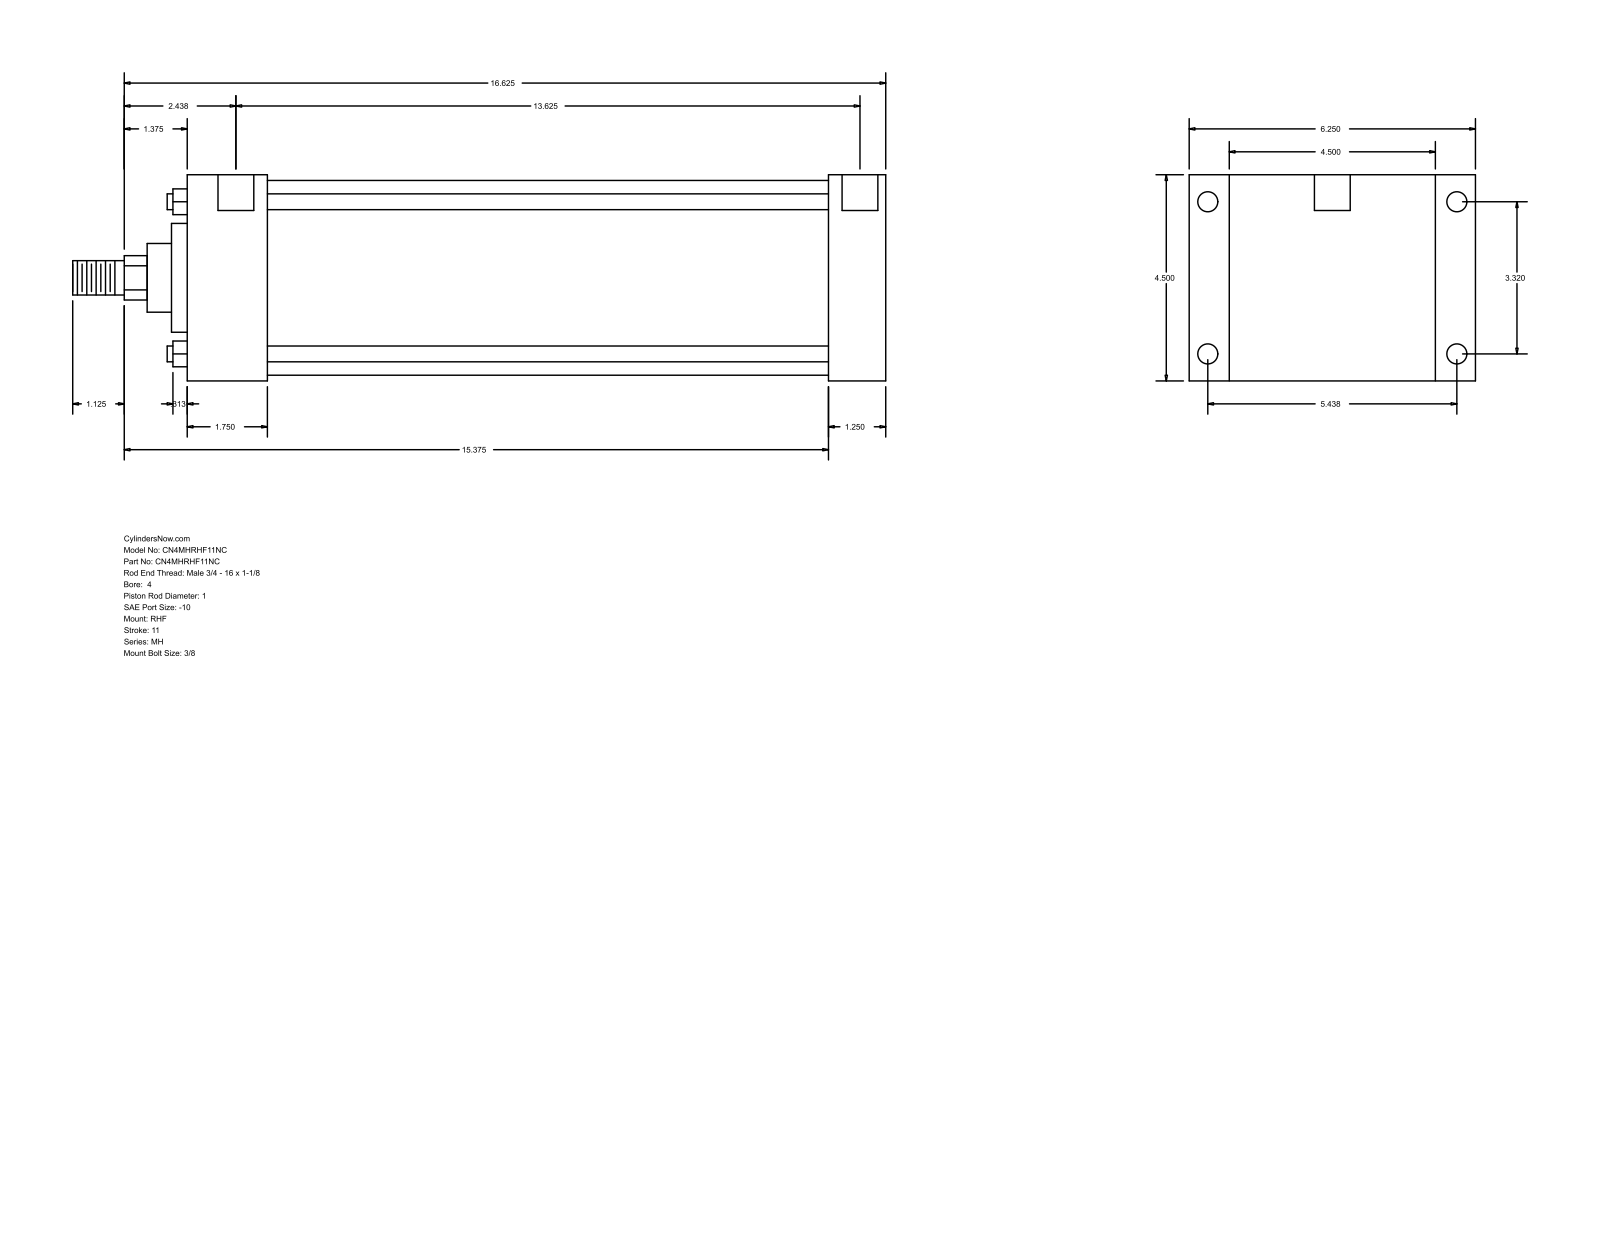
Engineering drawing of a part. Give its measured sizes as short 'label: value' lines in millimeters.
name: MH_RHF__0400_1
written by: GSSL Pune (CONFIG_CONTROL_DESIGN)
unit: mm
bodies: 0 solids, 90 faces (61 planar, 29 cylindrical, 0 other)
size: 450.85 × 158.75 × 114.3
holes: 4× ⌀8.73, 4× ⌀11.13, 2× ⌀19.84
bosses: 4× ⌀8.76, 1× ⌀107.95, 1× ⌀60.33, 1× ⌀38.1, 1× ⌀25.4, 1× ⌀19.05
rounds: 1× R12.29
face distances: 114.3, 387.35, 355.6, 31.75, 22.23, 136.53, 44.46, 311.14, 342.89, 158.76
hole spacings: 1.58, 84.32, 138.12, 161.82, 347.66, 349.24, 346.08
